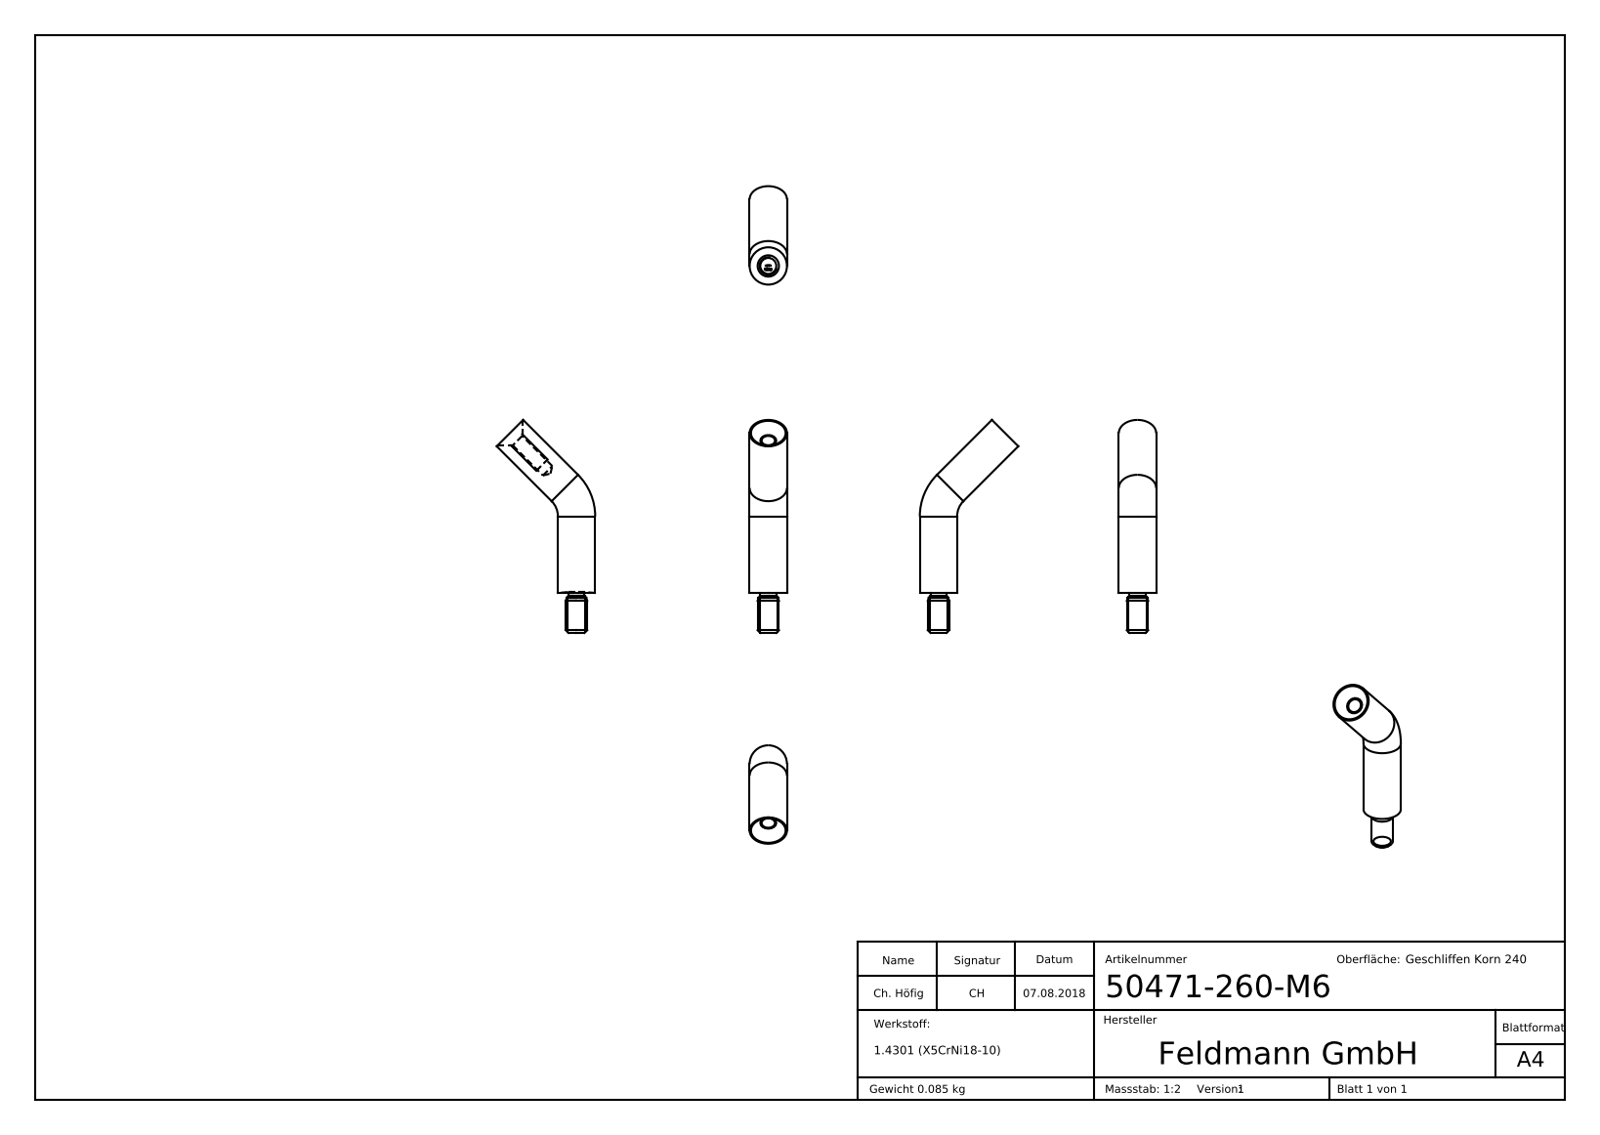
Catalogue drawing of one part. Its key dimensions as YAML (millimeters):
part_name: "50471-240-M6"
step_written_by: "SolidWorks 2015 (CONFIG_CONTROL_DESIGN)"
units: millimeters
bodies: {solids: 1, faces: 279, planar: 158, cylindrical: 10, other: 111}
overall_size: [79.95, 36.95, 14]
volume: 10820
surface_area: 4061
round_holes:
  - {diameter: 5, count: 1}
round_bosses_or_shafts:
  - {diameter: 14, count: 2}
  - {diameter: 8, count: 1}
  - {diameter: 6, count: 1}
face_to_face_distances: [1.33, 1.44, 1.13, 0.58, 0.42, 0.75, 1.35, 0.77, 0.55, 0.54]
